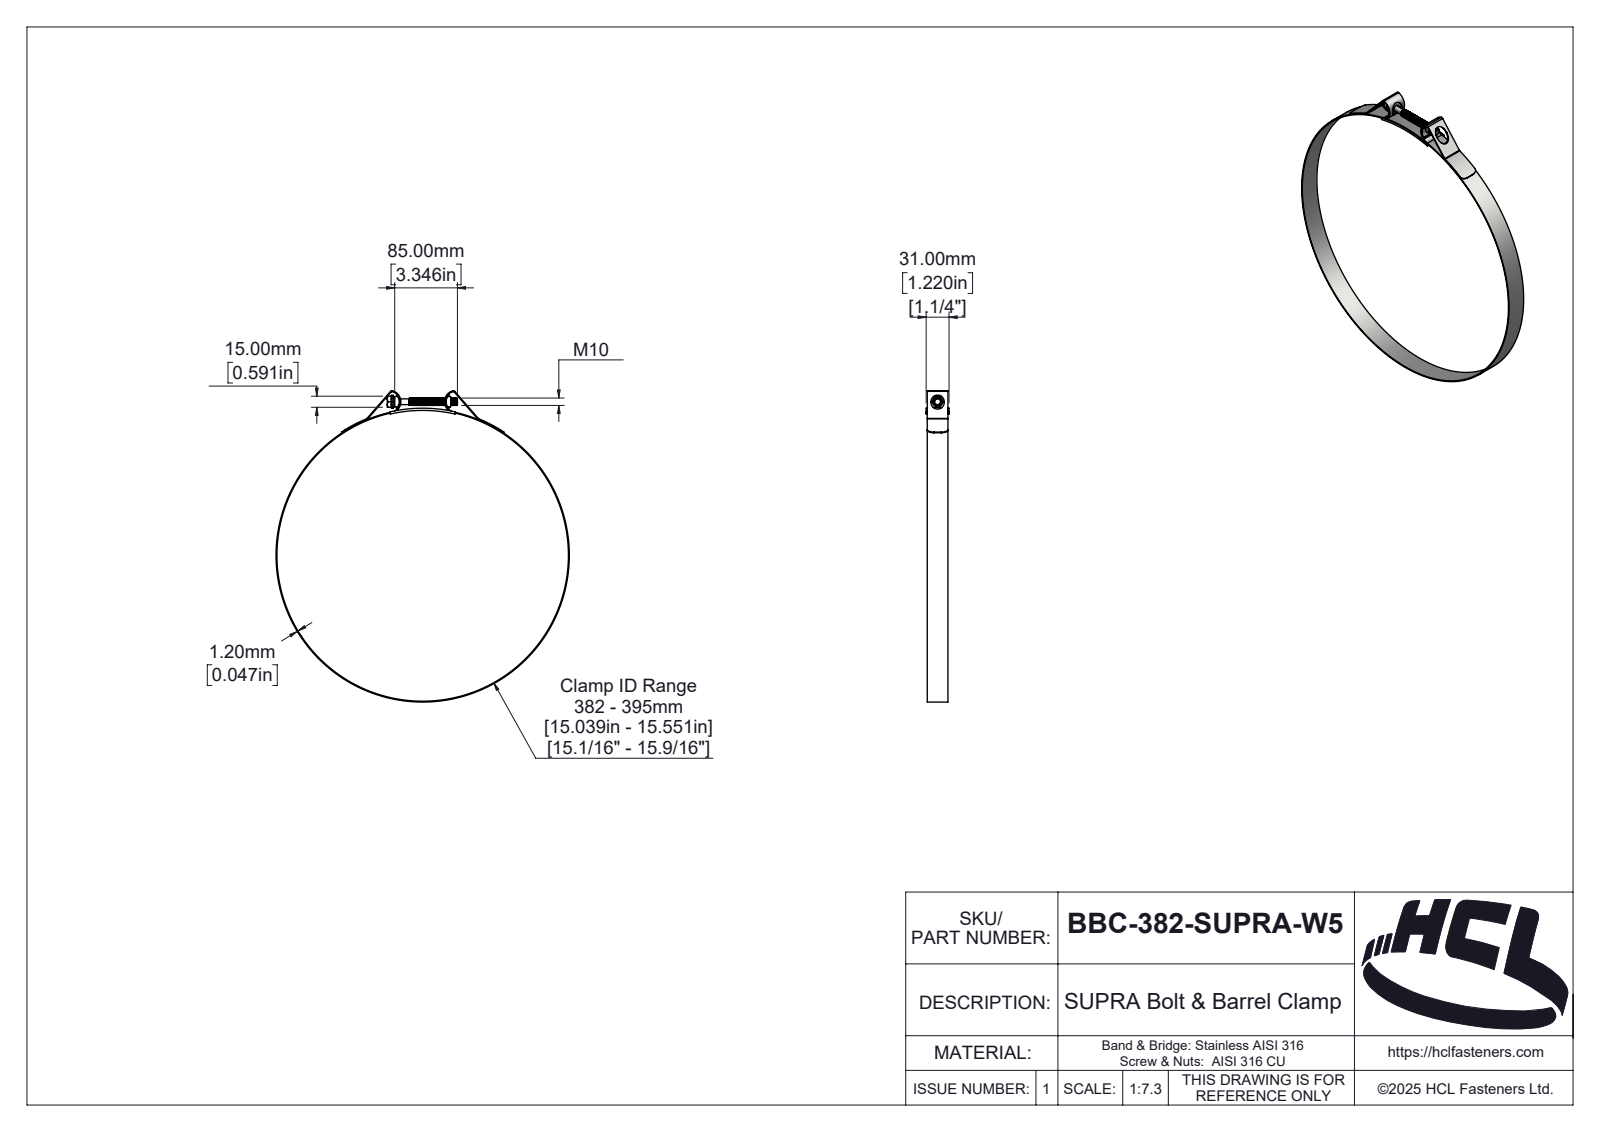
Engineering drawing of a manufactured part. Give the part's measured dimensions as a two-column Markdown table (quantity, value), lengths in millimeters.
| quantity | value |
| --- | --- |
| part name | BBC-382-SUPRA-W5 |
| STEP written by | SolidWorks 2025 (AUTOMOTIVE_DESIGN) |
| units | millimeters |
| bodies | 5 solids, 378 faces (50 planar, 241 cylindrical, 87 other) |
| overall size | 421.66 × 397.4 × 31 |
| volume | 59 145 mm³ |
| surface area | 94 768 mm² |
| round holes (diameter × count) | 395 × 1 |
| round bosses / shafts (diameter × count) | 397.4 × 1, 17.32 × 1, 14 × 1, 10 × 1, 7.8 × 1 |
| partial cylindrical surfaces (radius × count) | 1 × 4, 1.3 × 2, 2 × 2, 2.5 × 2, 3.2 × 2, 9 × 2, 13.03 × 2, 14.03 × 2 |
| main face-to-face distances | 1.2, 28, 1.5, 29.5, 29.8, 28.3, 31, 28.6, 12.5, 83.32 |
